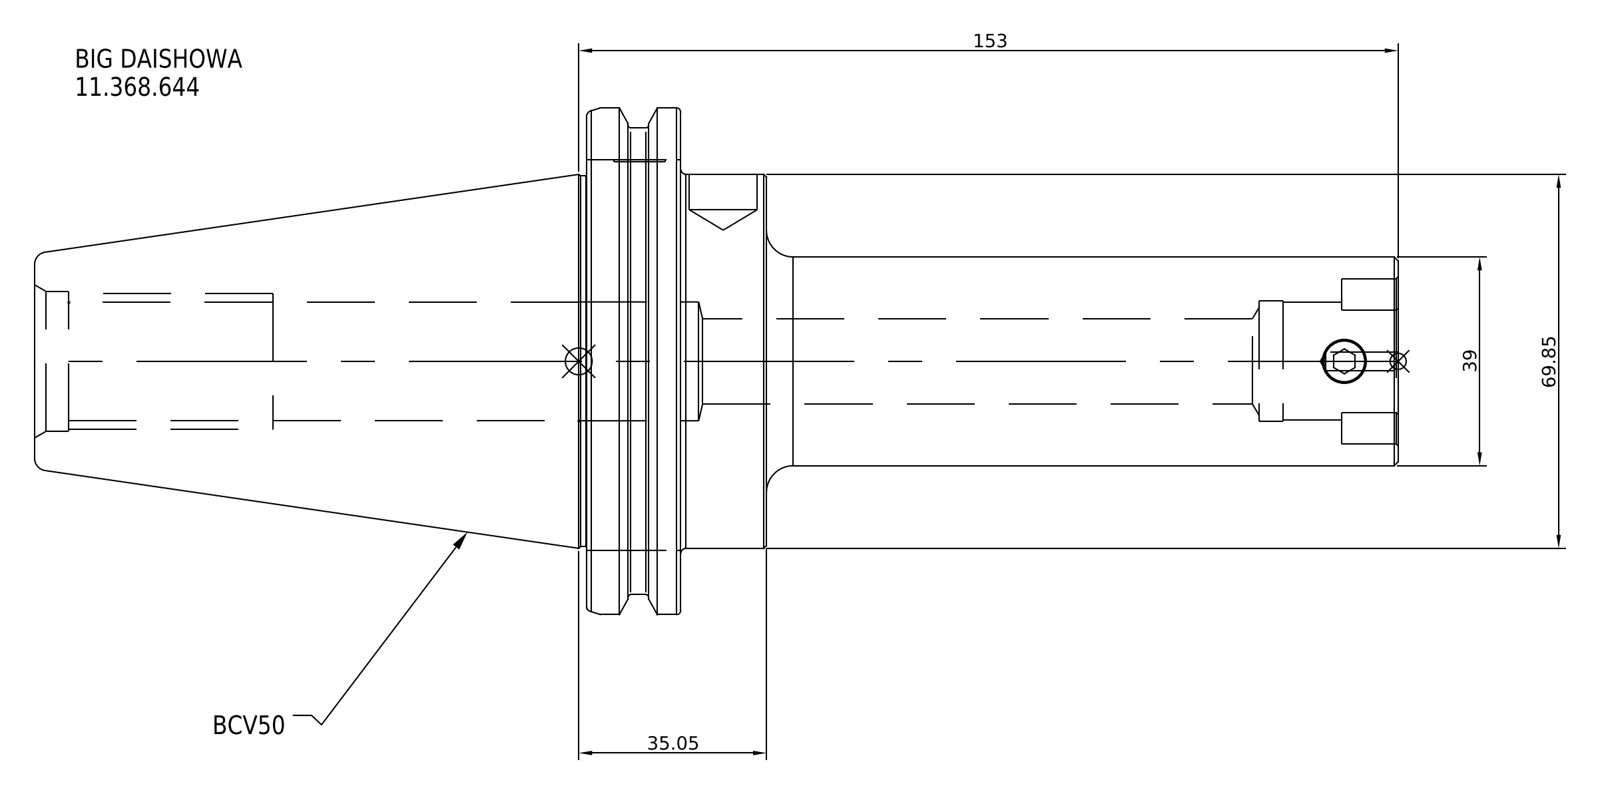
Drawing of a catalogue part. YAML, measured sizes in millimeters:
part_name: "11.368.644"
step_written_by: "SolidWorks 2021 (CONFIG_CONTROL_DESIGN)"
units: millimeters
bodies: {solids: 1, faces: 16, planar: 7, cylindrical: 6, other: 3}
overall_size: [254.6, 98.43, 98.43]
volume: 583442
surface_area: 55431
round_bosses_or_shafts:
  - {diameter: 98.43, count: 1}
  - {diameter: 91.29, count: 1}
  - {diameter: 69.85, count: 1}
  - {diameter: 39, count: 1}
face_to_face_distances: [17.55, 15.95, 33.5, 136.6, 120.65, 103.1, 118, 133.95, 151.5, 254.6]
